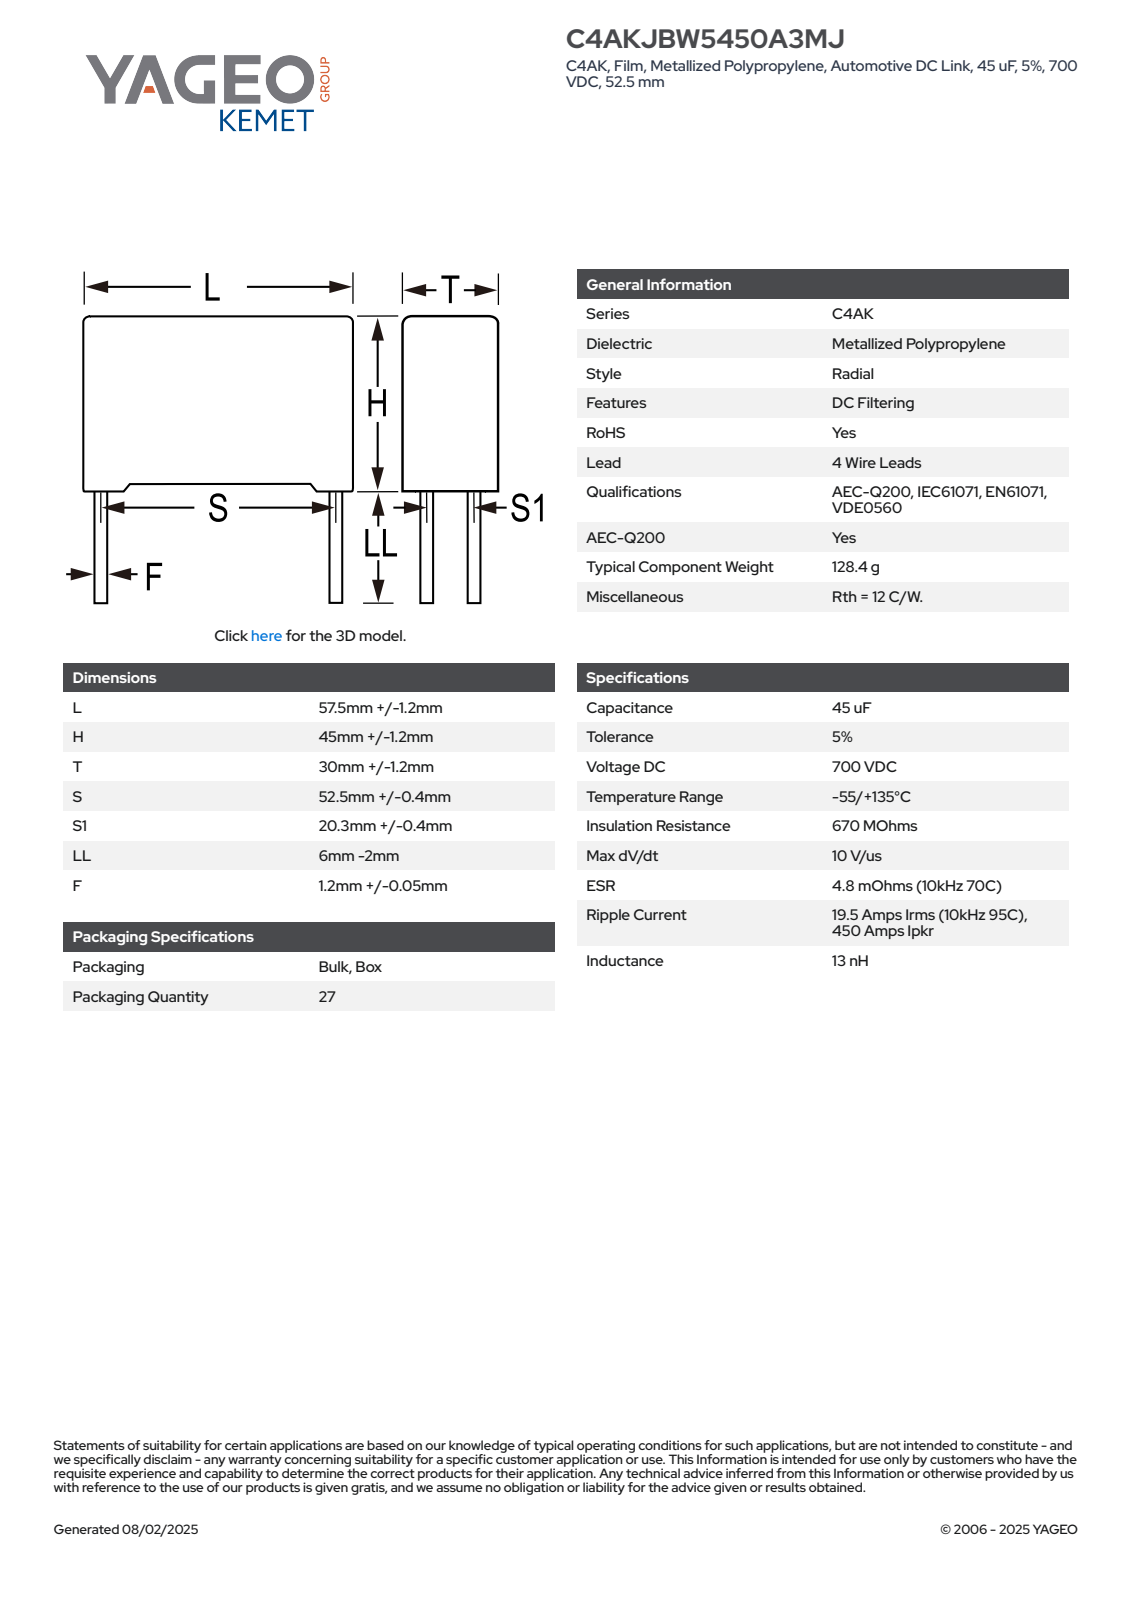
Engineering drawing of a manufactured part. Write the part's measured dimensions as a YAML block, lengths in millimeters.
part_name: "CFP_RB4_57.5X45X30_L58.7H46.2T31.2S52.5S120.3LL4F1.25"
step_written_by: "SolidWorks 2014 (AUTOMOTIVE_DESIGN)"
units: millimeters
bodies: {solids: 4, faces: 87, planar: 79, cylindrical: 8, other: 0}
overall_size: [58.7, 50.2, 31.2]
volume: 82377
surface_area: 12273
round_bosses_or_shafts:
  - {diameter: 1.25, count: 4}
face_to_face_distances: [31.2, 44.84, 58.7, 1.36, 46.2, 31.21, 1.92, 56.78, 54.86, 29.28]
